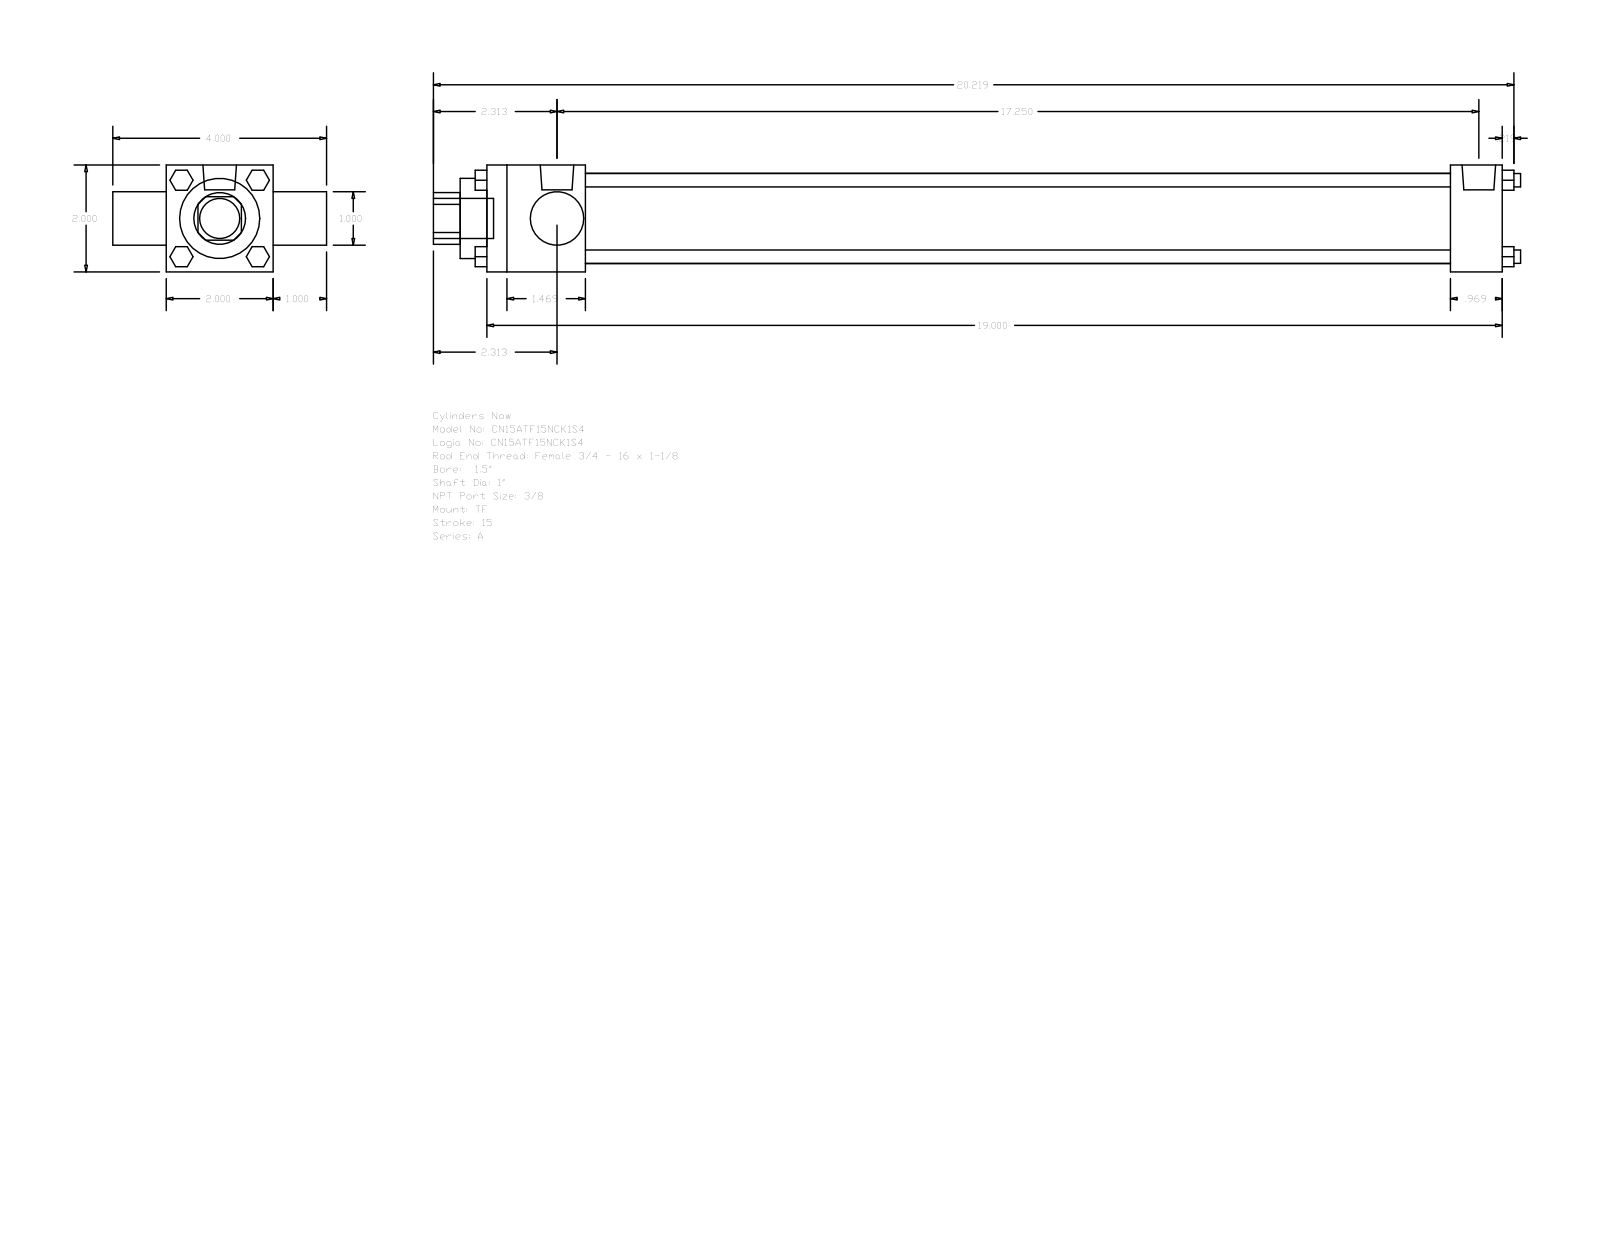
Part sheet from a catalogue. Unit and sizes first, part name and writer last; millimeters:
Units: millimetres
Overall size (bounding box): 516.73 × 101.6 × 50.8
Round holes (diameter × count): ⌀25.4 ×2, ⌀38.1 ×1, ⌀42.93 ×1
Round bosses / shafts (diameter × count): ⌀6.35 ×4, ⌀5.56 ×3, ⌀15.93 ×2, ⌀19.05 ×1
Partial cylindrical surfaces — rounded edges, fillets, slot ends (radius × count): R12.29 ×1
Main face-to-face distances: 50.8, 25.4, 482.6, 76.2, 46.83, 457.99, 411.16, 435.77, 24.61, 12.7
Bodies: 0 solids, 120 faces (92 planar, 28 cylindrical, 0 other)
Part name (STEP PRODUCT): A_TF__0150_1
STEP written by: GSSL Pune (CONFIG_CONTROL_DESIGN)
